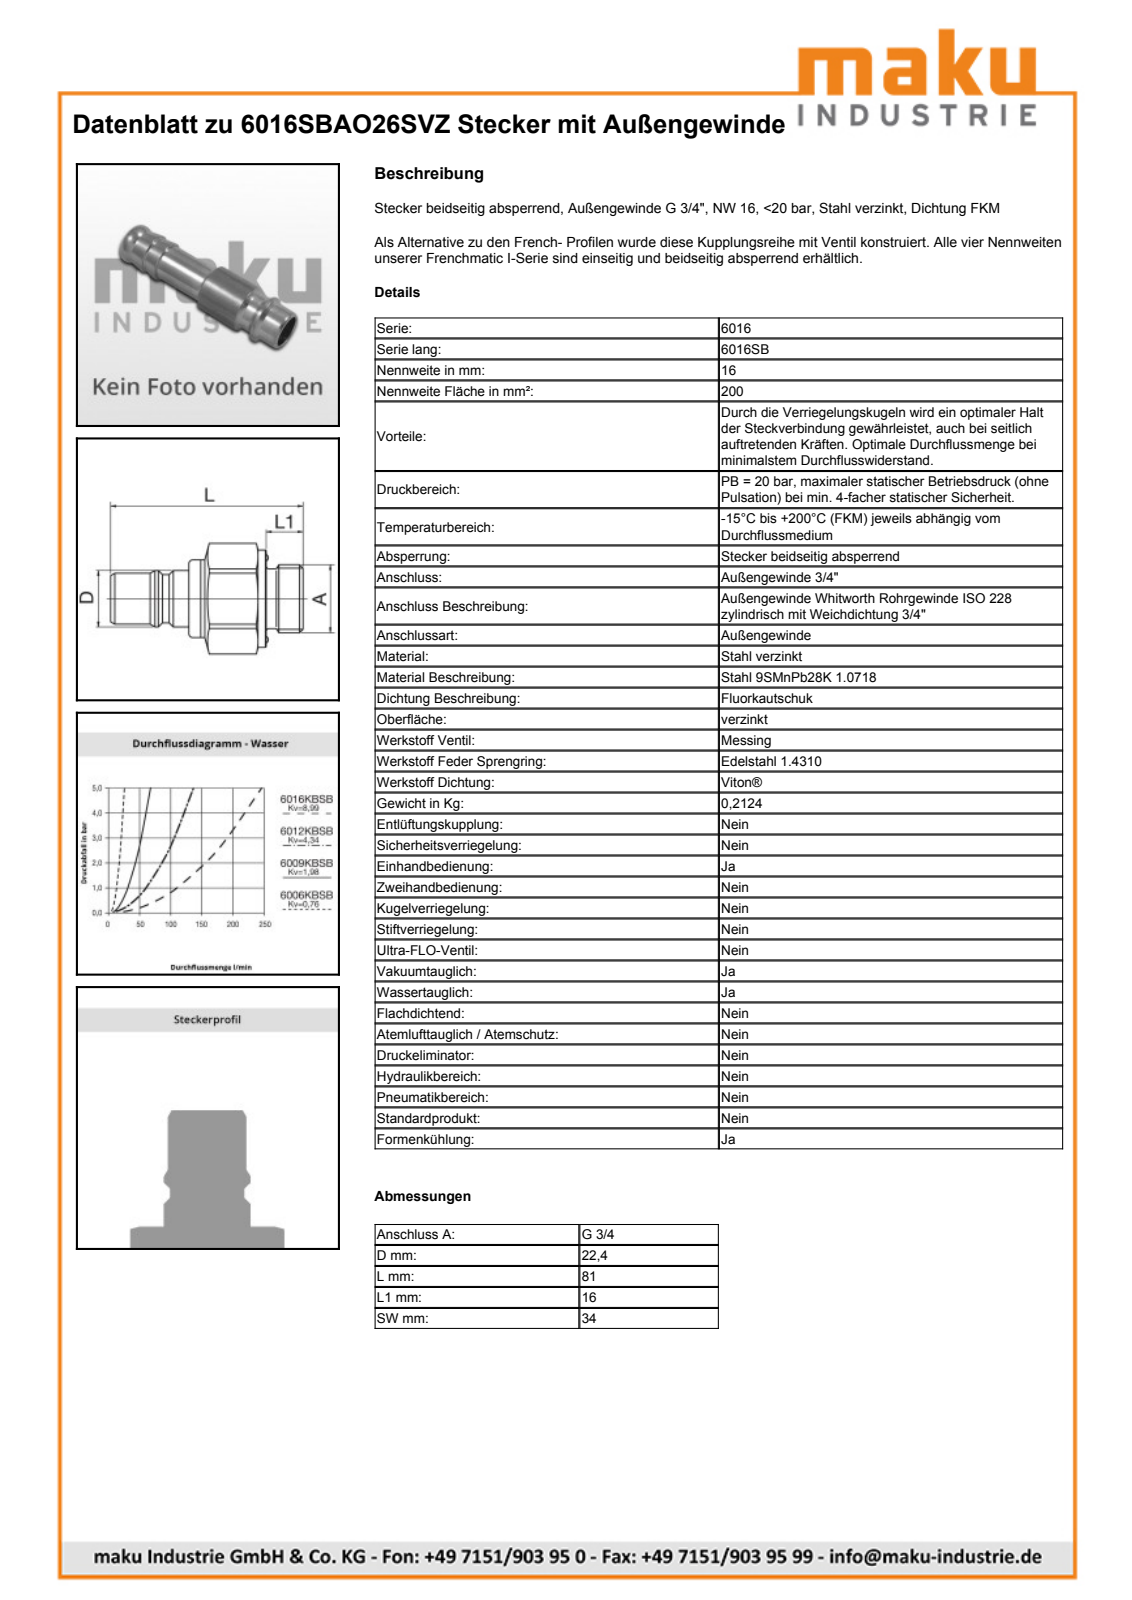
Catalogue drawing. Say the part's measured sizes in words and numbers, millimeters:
The part is named "D107573". Its 3-D file was written by "Autodesk Inventor 2013 (AUTOMOTIVE_DESIGN)". It is 1 solid with 59 faces: 15 planar, 23 cylindrical and 21 other. Overall it measures 81 by 37.48 by 37.08 millimeters. Its volume is 45 941 cubic millimeters and its surface area 14 227 square millimeters. Round holes: 1 of diameter 24.5, 1 of diameter 24.6, 1 of diameter 29, 1 of diameter 30.2, 1 of diameter 31.3. Round bosses or shafts: 1 of diameter 33.8, 1 of diameter 32, 1 of diameter 30, 1 of diameter 26.44, 1 of diameter 25.5, 1 of diameter 23.8, 1 of diameter 22.45, 1 of diameter 20.95. Partial cylindrical surfaces (rounded edges, fillets, slot ends): 1 of radius 19.05. The main face-to-face distances are 34, 81, 62.8, 18.2, 31.5, 31.3, 49.5, 65, 33.5, 2.2.
